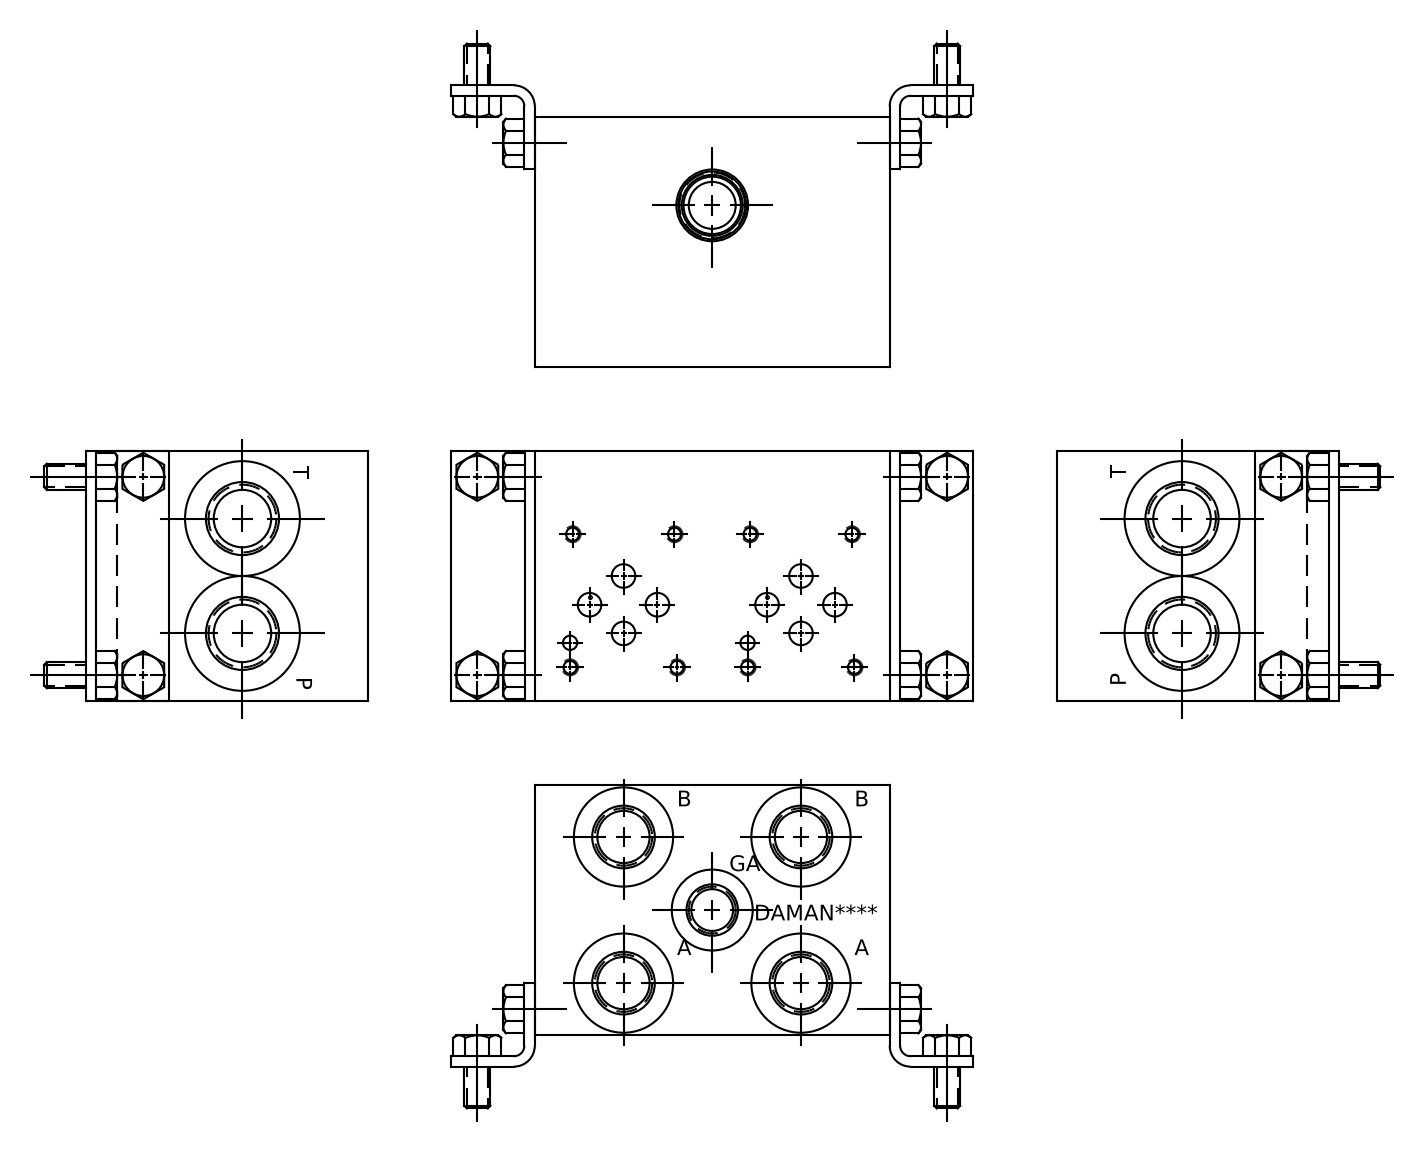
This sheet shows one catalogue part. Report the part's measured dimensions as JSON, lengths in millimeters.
{"part_name": "Part_AD03P022S_S_3D", "step_written_by": "Autodesk Inventor 2020 (CONFIG_CONTROL_DESIGN)", "units": "millimeters", "bodies": {"solids": 1, "faces": 689, "planar": 364, "cylindrical": 85, "other": 240}, "overall_size": [107.95, 76.2, 76.2], "volume_mm3": 536777, "surface_area_mm2": 64715, "round_holes": [[3.78, 8], [4.83, 8], [7.14, 6], [15.88, 4], [17.5, 4], [19.05, 4], [19.25, 4], [30.63, 4], [3.96, 2], [6.35, 2], [6.53, 2], [7.92, 2]], "face_to_face_distances": [76.2, 107.95, 0.79, 75.41, 107.16, 106.37, 17.45, 90.5, 16.66, 89.71], "hole_center_spacings": [53.97, 19.95, 22.05, 33.55, 40.49, 51.45, 53.98, 7.49]}
